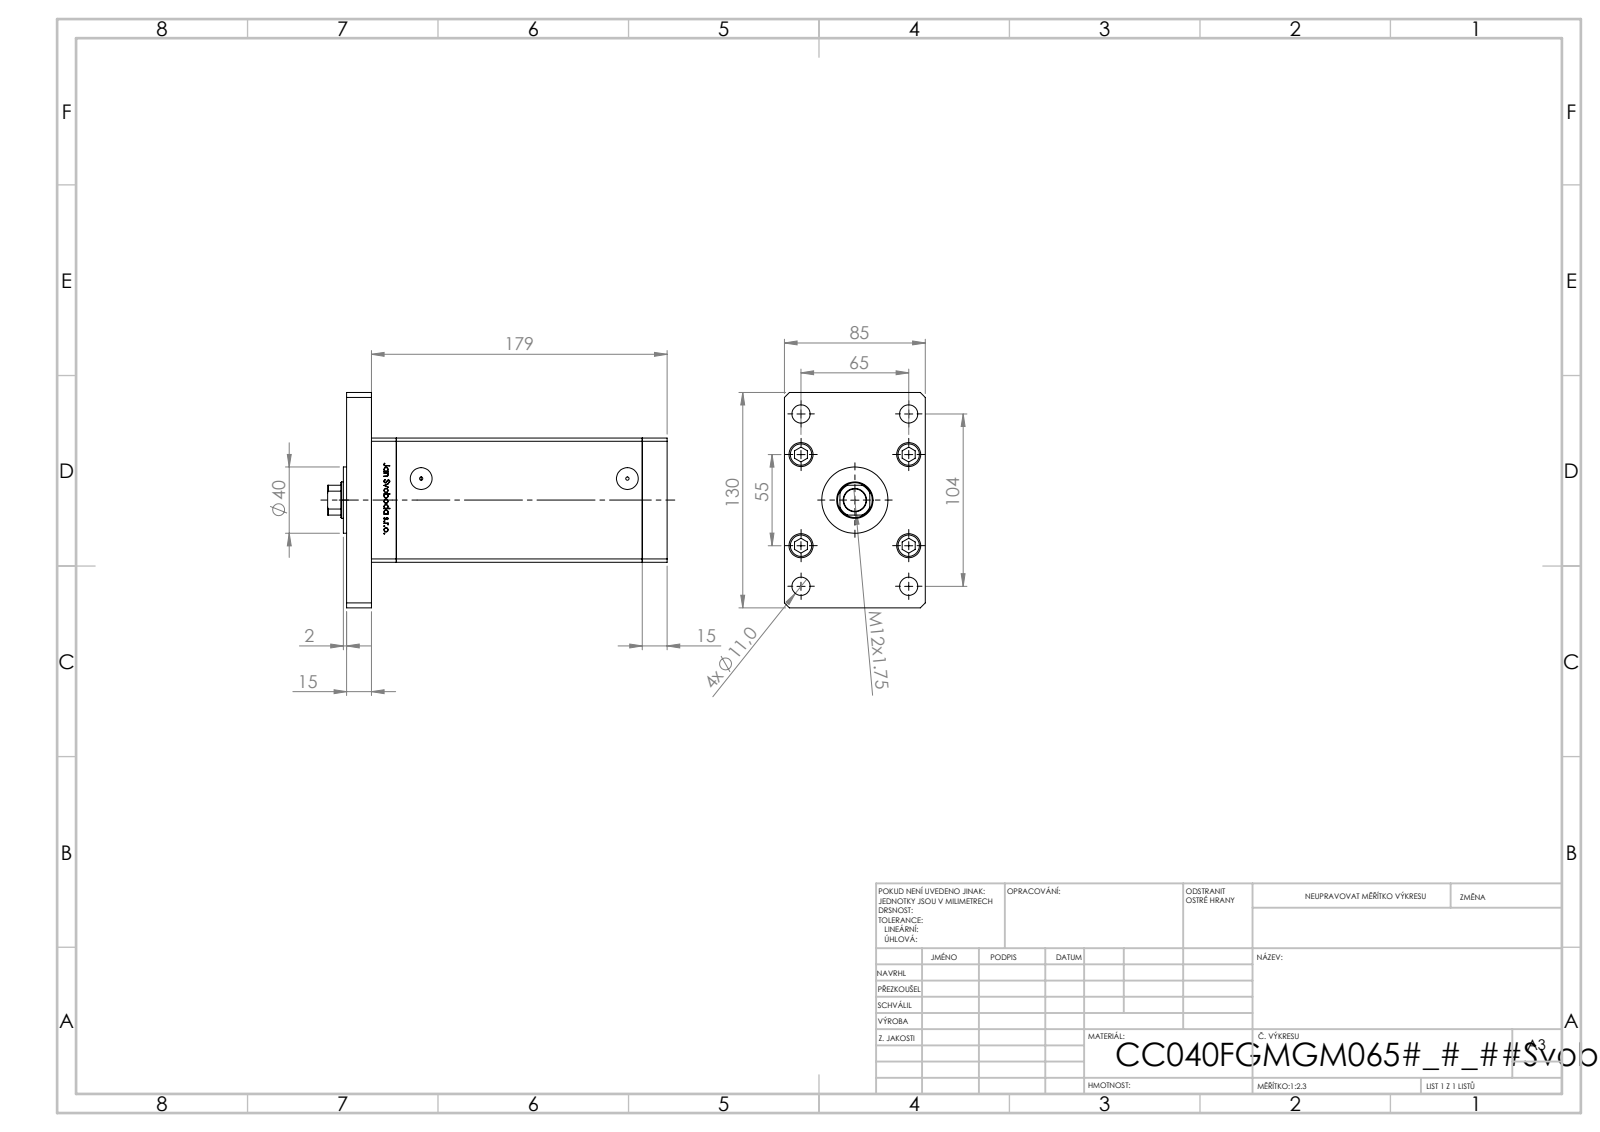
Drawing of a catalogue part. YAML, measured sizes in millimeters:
part_name: "V220C BACK_F; V220C_VC_F; V220C_FRONT_F; V220C_F (+2 more)"
step_written_by: "SolidWorks 2019 (CONFIG_CONTROL_DESIGN)"
units: millimeters
bodies: {solids: 19, faces: 1308, planar: 515, cylindrical: 187, other: 606}
overall_size: [205, 130, 85]
volume: 1165000
surface_area: 198848
round_holes:
  - {diameter: 11, count: 9}
  - {diameter: 15.5, count: 5}
  - {diameter: 10, count: 4}
  - {diameter: 14.5, count: 4}
  - {diameter: 2, count: 2}
  - {diameter: 13.16, count: 2}
  - {diameter: 13.5, count: 1}
  - {diameter: 22, count: 1}
  - {diameter: 23.5, count: 1}
round_bosses_or_shafts:
  - {diameter: 8, count: 9}
  - {diameter: 14.5, count: 5}
  - {diameter: 40, count: 1}
partial_cylinders:
  - {radius: 0.93, count: 2}
  - {radius: 10.5, count: 1}
face_to_face_distances: [15, 85, 163.5, 178.5, 75, 148.5, 30, 193.5, 10.5, 27.5]
hole_center_spacings: [28, 24.5, 42.57, 61.32, 65, 69.46, 79.5, 102.69]
